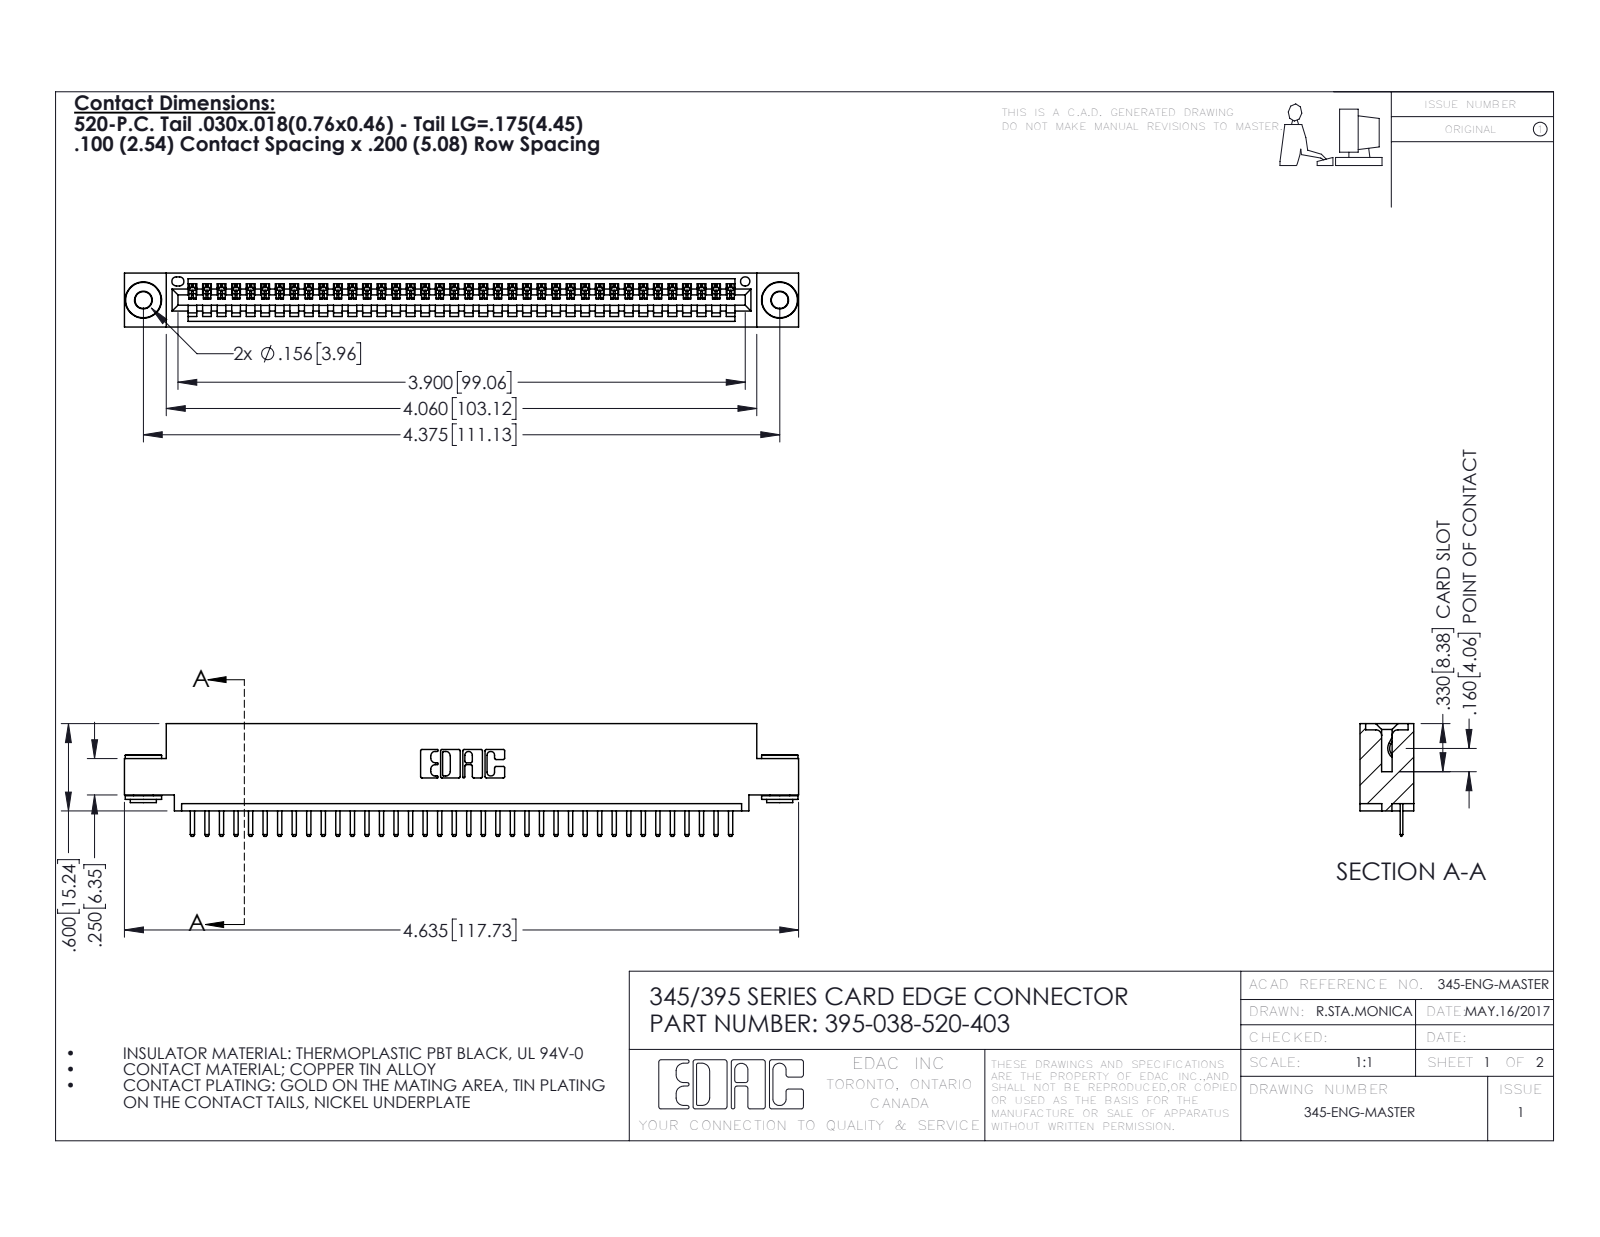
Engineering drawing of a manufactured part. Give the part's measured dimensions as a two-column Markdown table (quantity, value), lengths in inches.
| quantity | value |
| --- | --- |
| part name | 345-292-001_345-293-120; 345 Part_0.110 Offset - 0.156 Dia-TH; 345-250-002_345-250-002-102; 395-038-520-403 |
| STEP written by | SolidWorks 2016 (CONFIG_CONTROL_DESIGN) |
| units | inches |
| bodies | 41 solids, 2524 faces (1690 planar, 826 cylindrical, 8 other) |
| overall size | 4.635 × 0.775 × 0.37 |
| volume | 0.67 in³ |
| surface area | 22.45 in² |
| round holes (diameter × count) | 0.116 × 2, 0.156 × 2, 0.064 × 1 |
| round bosses / shafts (diameter × count) | 0.25 × 2, 0.18 × 2, 0.136 × 2 |
| partial cylindrical surfaces (radius × count) | 0.01 × 78, 0.006 × 76, 0.01 × 22, 0.007 × 6, 0.031 × 6, 0.026 × 3, 0.031 × 2, 0.04 × 2 |
| main face-to-face distances | 0.072, 0.298, 0.37, 0.2, 0.025, 0.098, 0.272, 0.225, 0.072, 0.149 |
| hole center spacings | 0.27, 4.139, 4.375 |
